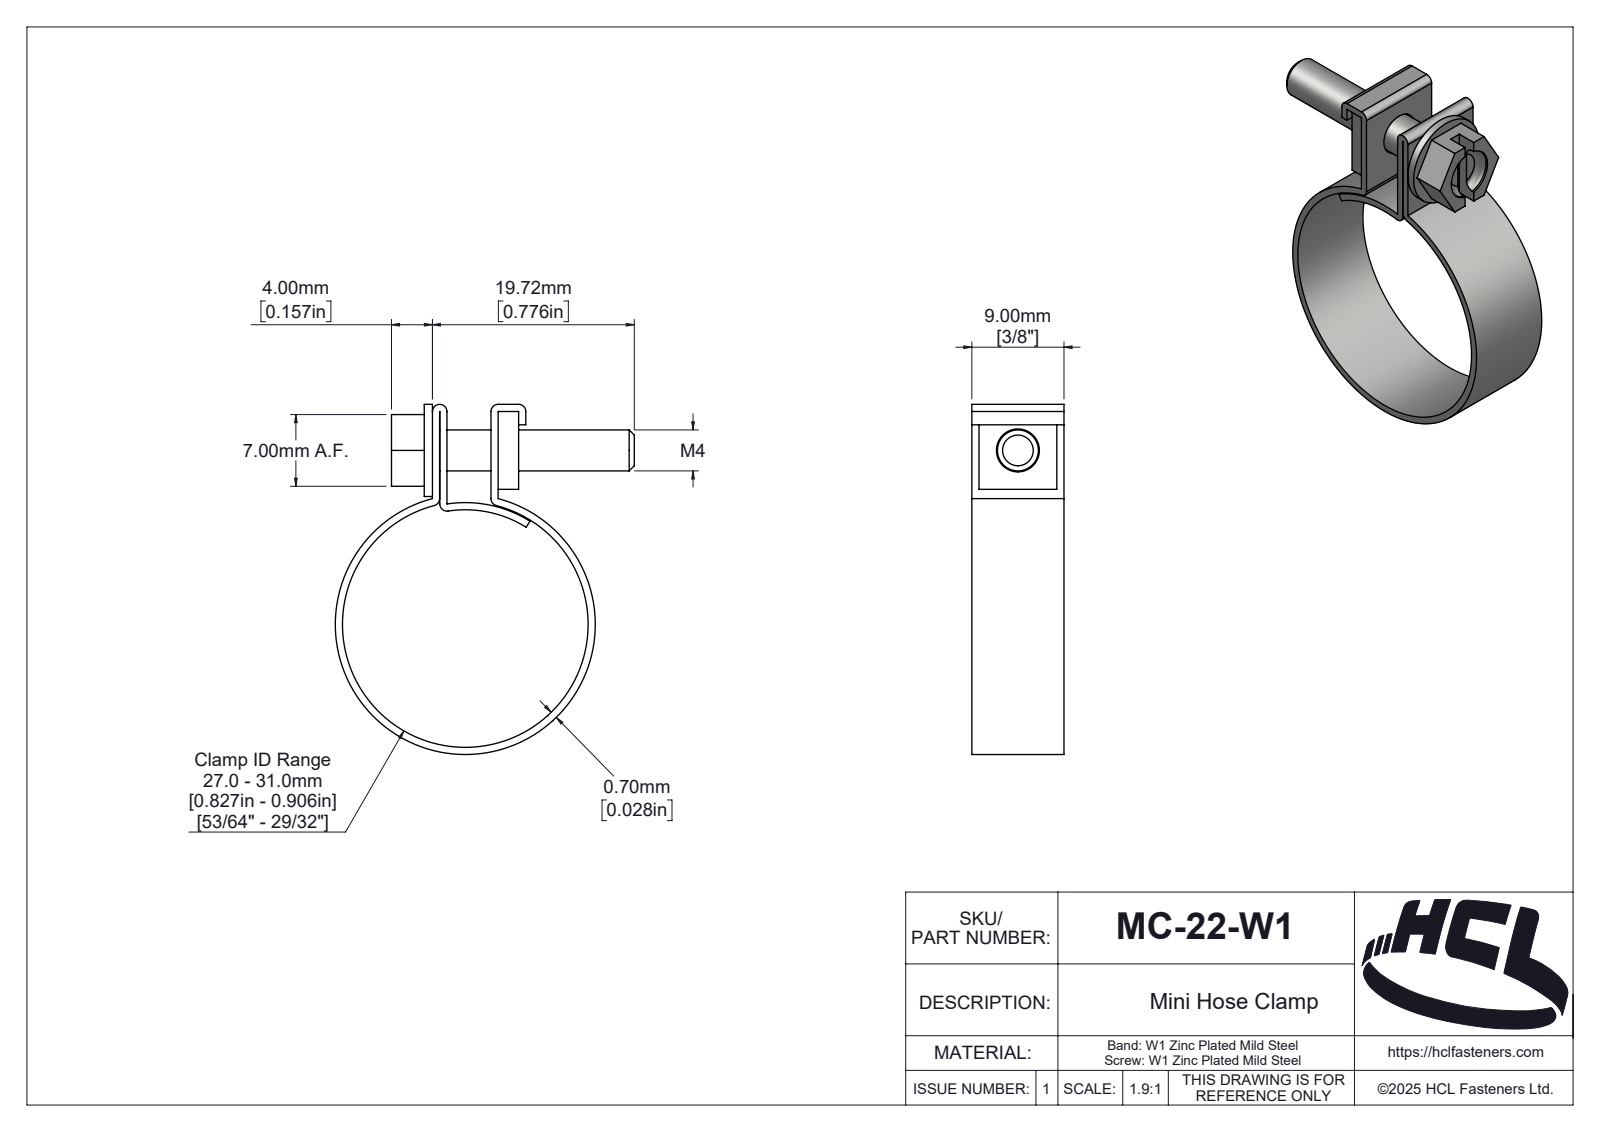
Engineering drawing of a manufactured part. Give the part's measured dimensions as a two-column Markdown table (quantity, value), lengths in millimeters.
| quantity | value |
| --- | --- |
| part name | MC-22-W1 |
| STEP written by | SolidWorks 2025 (AUTOMOTIVE_DESIGN) |
| units | millimeters |
| bodies | 3 solids, 170 faces (38 planar, 79 cylindrical, 53 other) |
| overall size | 34.19 × 29.21 × 9 |
| volume | 1 172 mm³ |
| surface area | 2 814 mm² |
| round holes (diameter × count) | 4.2 × 1, 5 × 1, 24 × 1 |
| round bosses / shafts (diameter × count) | 25.4 × 1, 9 × 1, 4 × 1 |
| partial cylindrical surfaces (radius × count) | 0.7 × 5, 0.2 × 1, 0.71 × 1, 0.81 × 1, 1.01 × 1, 1.06 × 1, 1.28 × 1, 1.81 × 1 |
| main face-to-face distances | 0.7, 5, 0.72, 5.72, 6.42, 7, 9, 2, 2.7, 8.42 |
